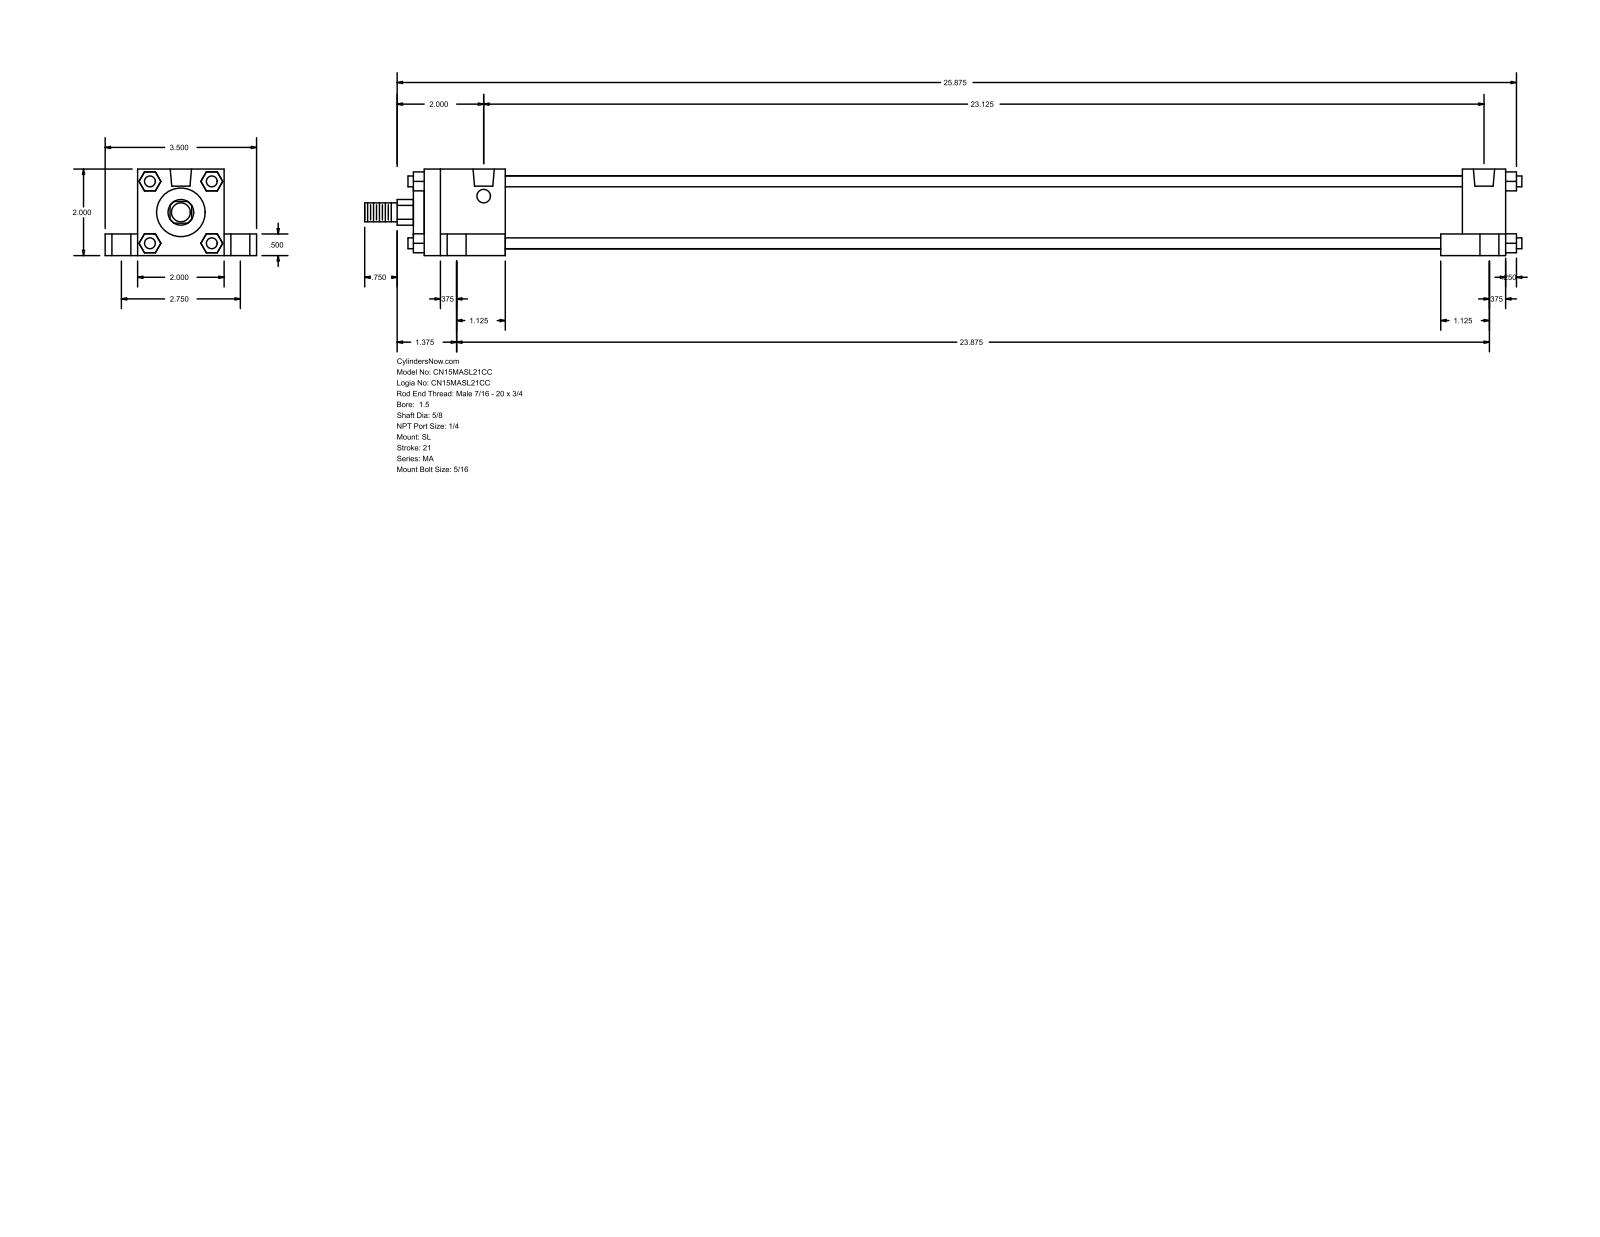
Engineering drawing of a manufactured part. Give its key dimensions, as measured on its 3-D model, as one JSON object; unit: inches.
{"part_name": "MA_SL__0150_0.625", "step_written_by": "GSSL Pune (CONFIG_CONTROL_DESIGN)", "units": "inches", "bodies": {"solids": 0, "faces": 148, "planar": 112, "cylindrical": 36, "other": 0}, "overall_size": [26.75, 3.5, 2], "round_holes": [[0.313, 4], [0.437, 4], [0.687, 4], [0.492, 2]], "round_bosses_or_shafts": [[0.25, 4], [1.69, 1], [1.125, 1], [0.625, 1], [0.437, 1]], "partial_cylinders_radius": [[0.297, 1]], "face_to_face_distances": [2, 0.75, 1.5, 25, 2.75, 0.5, 0.375, 1, 0.25, 25.25], "hole_center_spacings": [1.38, 1.51, 2.75, 23.125, 23.291, 23.79, 23.875, 24.033]}
